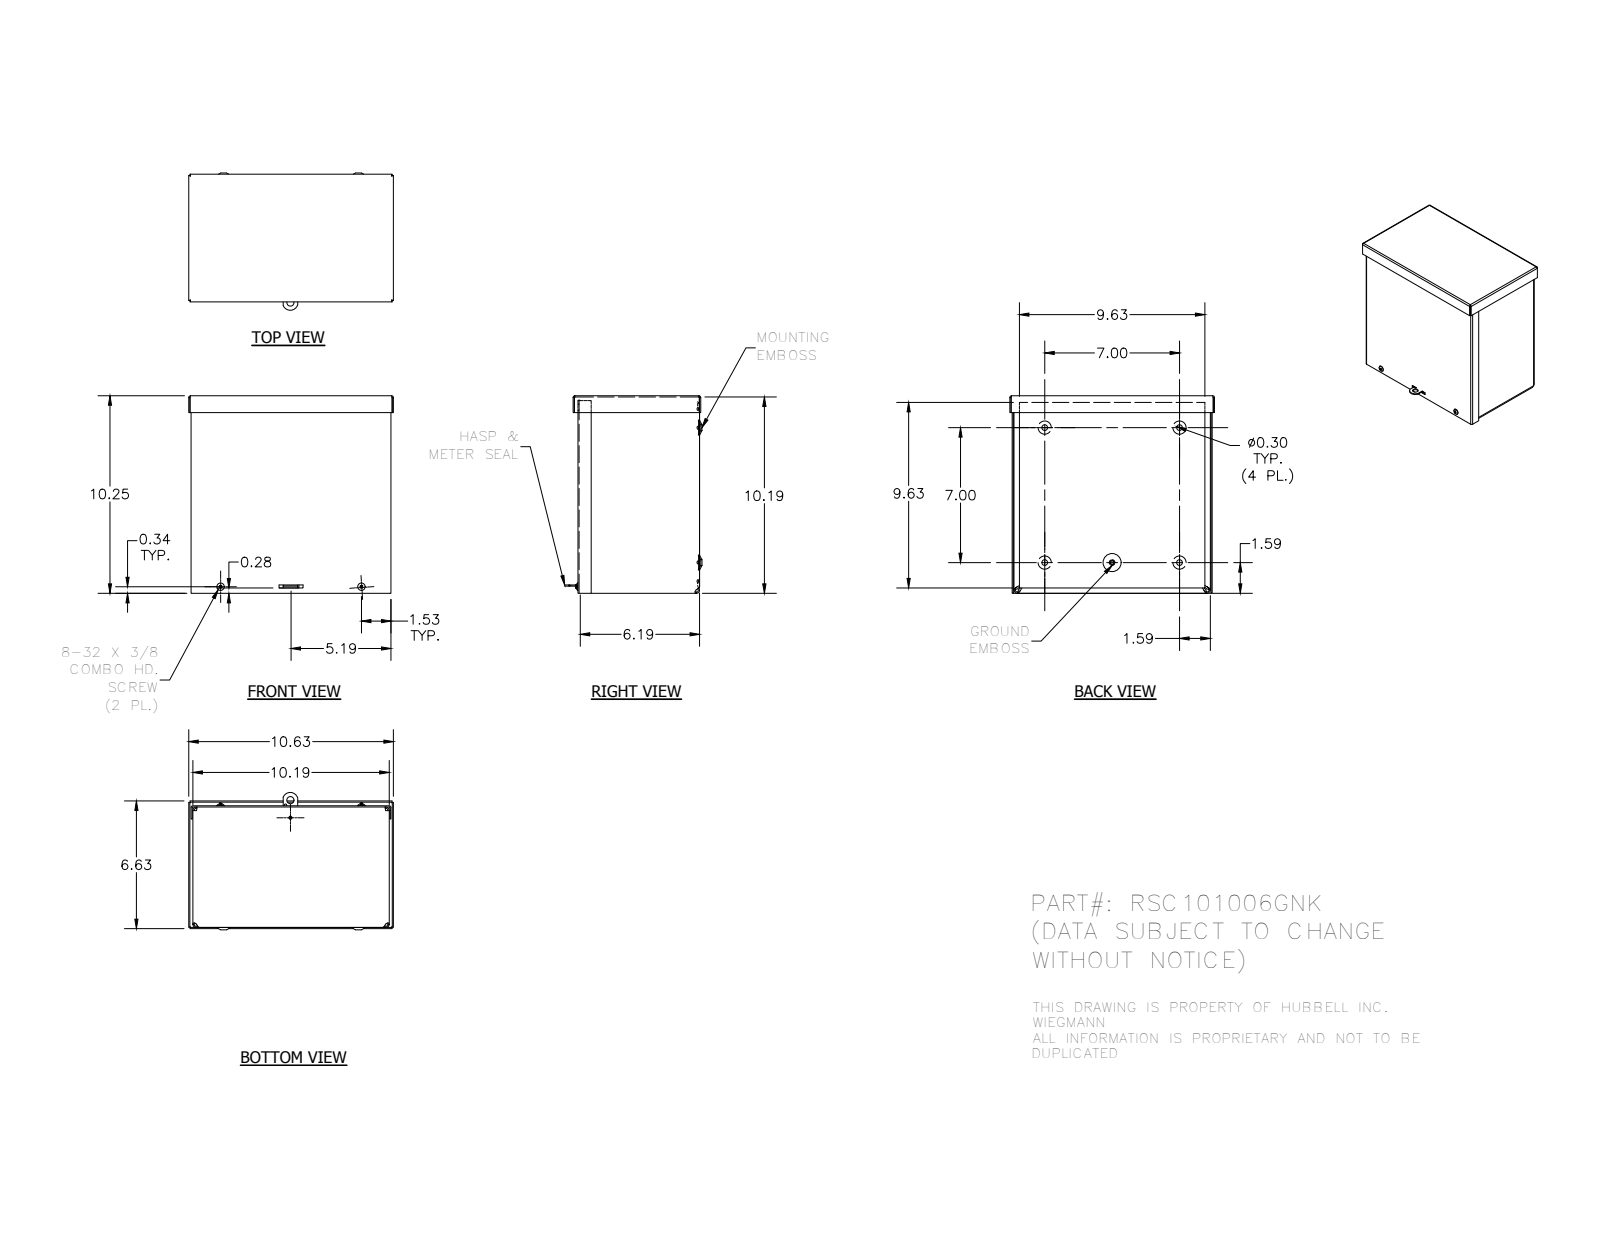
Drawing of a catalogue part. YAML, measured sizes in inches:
part_name: "RSC101006GNK_WRAP; RSC1010GNK_LID; RSC1006GNK_CAP; 3183 (+3 more)"
step_written_by: "Autodesk Inventor 2014 (AUTOMOTIVE_DESIGN)"
units: inches
bodies: {solids: 7, faces: 377, planar: 163, cylindrical: 78, other: 136}
overall_size: [10.625, 10.25, 7.125]
volume: 37.95
surface_area: 1239
round_holes:
  - {diameter: 0.3, count: 4}
  - {diameter: 0.313, count: 4}
  - {diameter: 0.125, count: 2}
  - {diameter: 0.148, count: 2}
  - {diameter: 0.156, count: 1}
  - {diameter: 0.165, count: 1}
  - {diameter: 0.375, count: 1}
round_bosses_or_shafts:
  - {diameter: 0.384, count: 2}
  - {diameter: 0.164, count: 2}
  - {diameter: 0.228, count: 1}
partial_cylinders:
  - {radius: 0.031, count: 8}
  - {radius: 0.093, count: 8}
  - {radius: 0.125, count: 8}
  - {radius: 0.187, count: 8}
  - {radius: 0.055, count: 4}
  - {radius: 0.062, count: 4}
  - {radius: 0.094, count: 4}
  - {radius: 0.117, count: 4}
face_to_face_distances: [0.062, 10.126, 0.062, 6.249, 10.188, 6.187, 0.063, 0.124, 6.312, 6.25]
hole_center_spacings: [7, 1.072, 1.261, 3.5, 7.313, 7.826, 8.063, 8.253]
